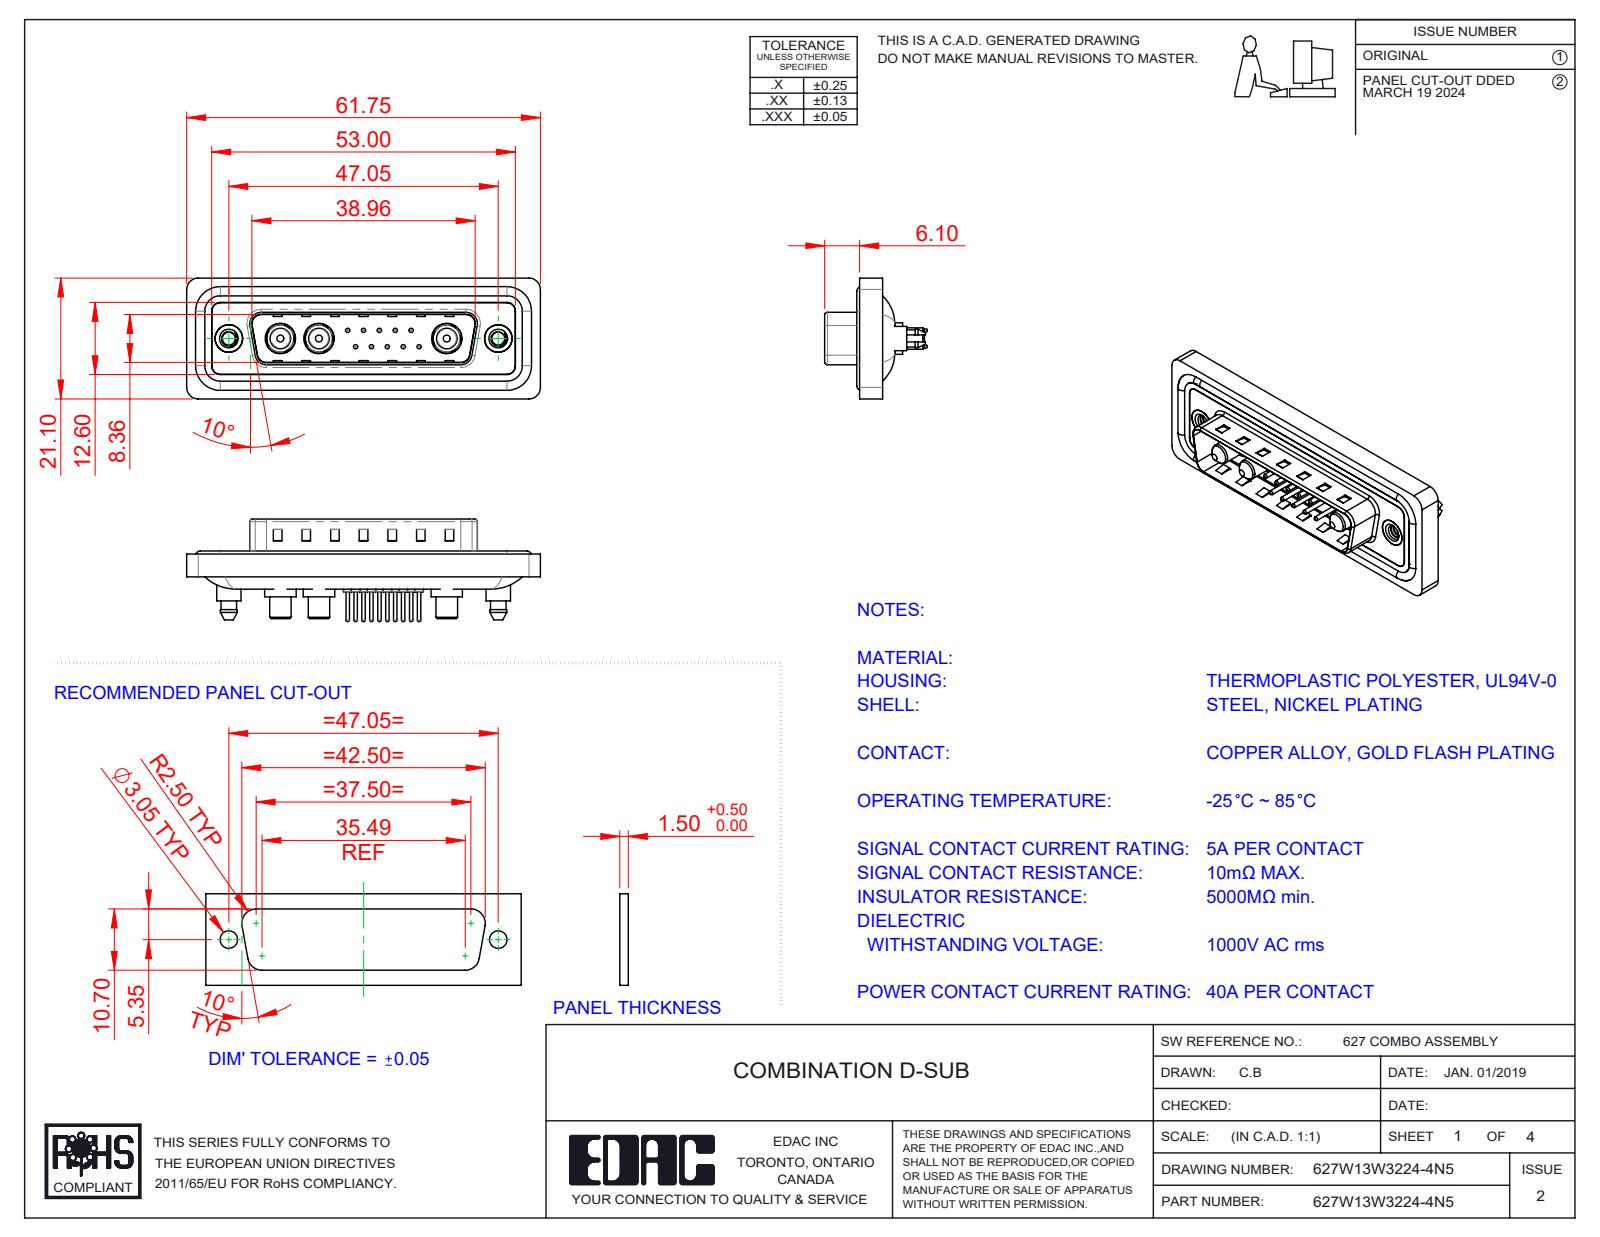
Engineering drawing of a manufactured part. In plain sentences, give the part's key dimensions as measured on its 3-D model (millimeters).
The part is named "627Combo Contact Row 1_24; 627W13W3224-4N5; 627Combo Shell Front_25 Contacts; 627Combo Housing_13W3 (+5 more)". Its 3-D file was written by "SolidWorks 2023 (CONFIG_CONTROL_DESIGN)". It is 23 solids with 1020 faces: 325 planar, 417 cylindrical and 278 other. Overall it measures 61.75 by 21.1 by 17.9 millimeters. Its volume is 7 524 cubic millimeters and its surface area 12 240 square millimeters. Round holes: 10 of diameter 0.75, 10 of diameter 1.6, 10 of diameter 2, 3 of diameter 4.85, 3 of diameter 5.3, 2 of diameter 2.26, 2 of diameter 4, 2 of diameter 4.8, 2 of diameter 5. Round bosses or shafts: 10 of diameter 1.5, 10 of diameter 0.6, 4 of diameter 1.6, 3 of diameter 5.5, 3 of diameter 5.2, 3 of diameter 4.75, 3 of diameter 3.75, 3 of diameter 3.6. Partial cylindrical surfaces (rounded edges, fillets, slot ends): 24 of radius 1.5, 18 of radius 2, 10 of radius 1.6, 8 of radius 0.5, 4 of radius 0.25, 4 of radius 0.6, 4 of radius 0.65, 4 of radius 0.9. The main face-to-face distances are 0.4, 1.5, 1.1, 1.6, 0.5, 3.1, 2.9, 0.82, 9.58, 4.1. The hole center spacings are 3.16, 2.77, 5.04, 5.54, 7.49, 5.03, 8.31, 10.11.
